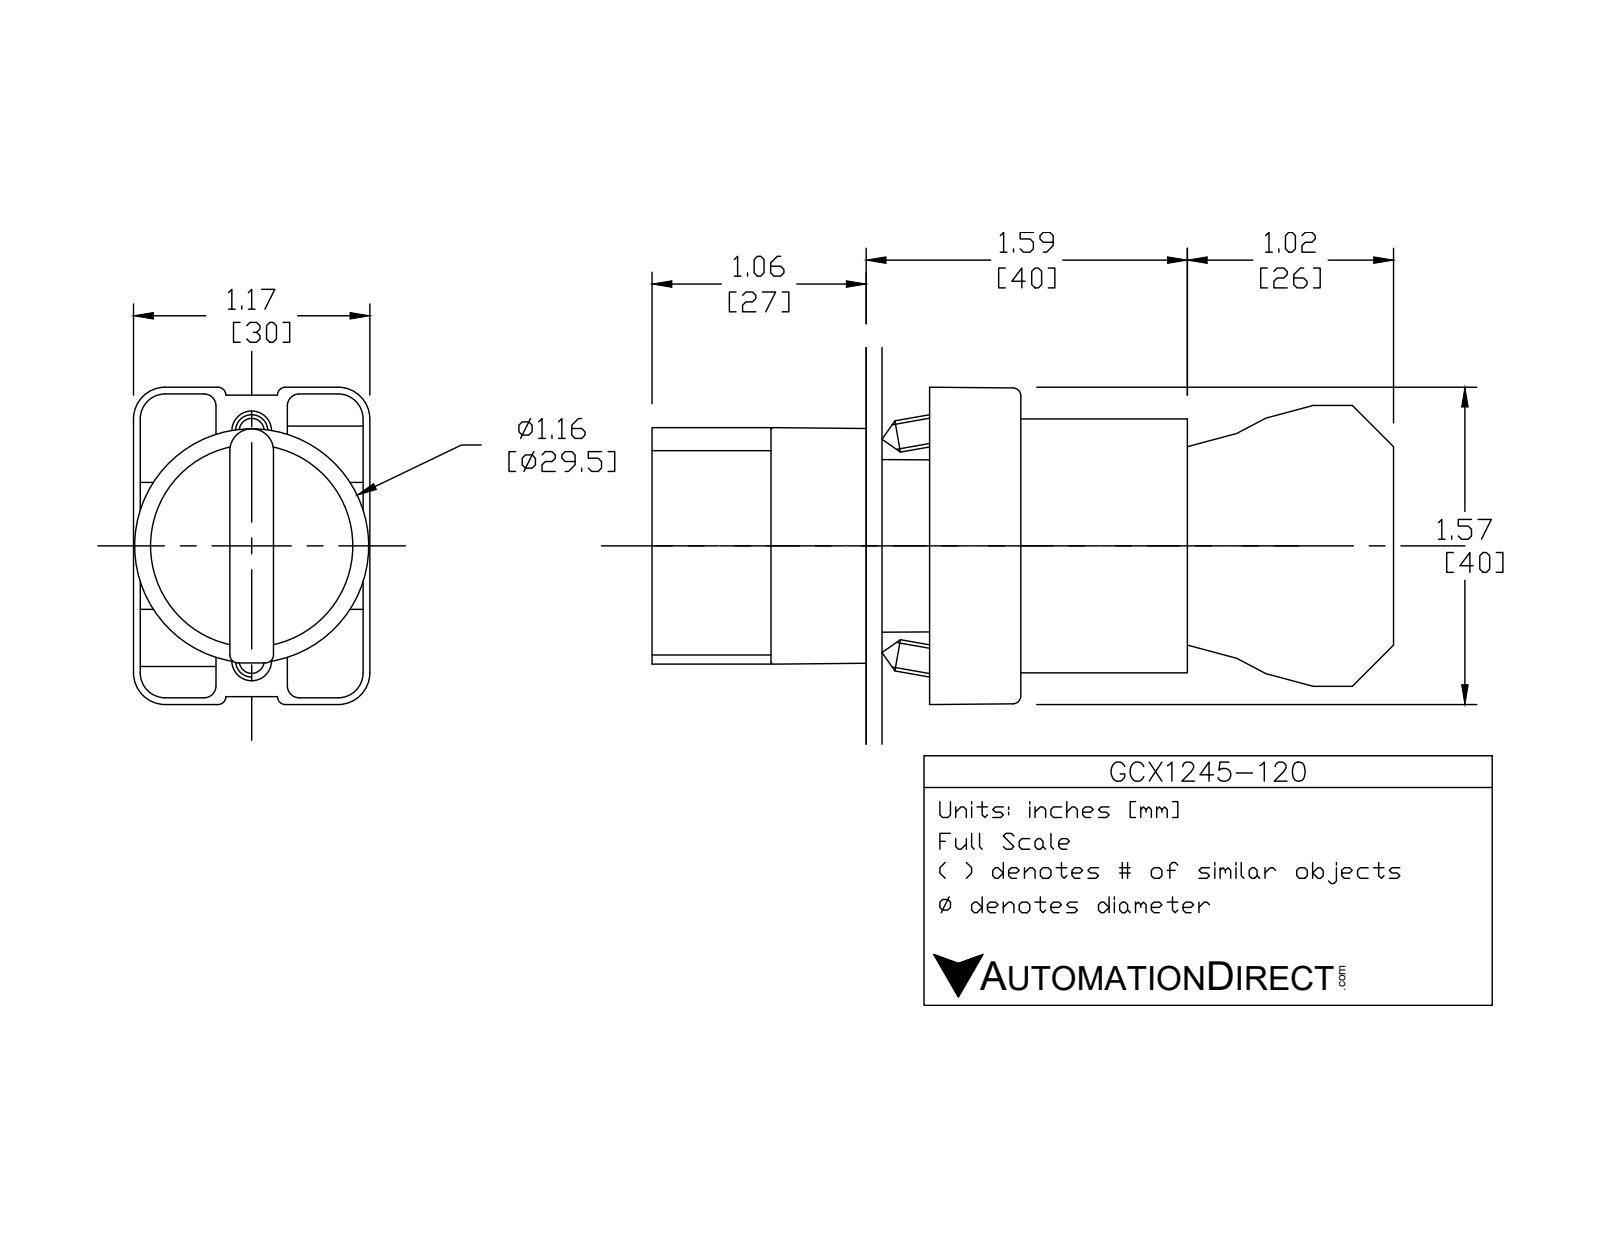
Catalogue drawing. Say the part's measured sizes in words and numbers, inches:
The part is named "ECX1050; ecx1040; GCX1245-120; ecx1029 (+1 more)". Its 3-D file was written by "SolidWorks 2016 (AUTOMOTIVE_DESIGN)". It is 8 solids with 445 faces: 263 planar, 151 cylindrical and 31 other. Overall it measures 3.653 by 1.581 by 1.177 inches. Its volume is 2.799 cubic inches and its surface area 39 square inches. Round holes: 2 of diameter 0.079, 2 of diameter 0.124, 2 of diameter 0.13, 1 of diameter 0.087, 1 of diameter 0.197, 1 of diameter 0.469, 1 of diameter 0.878, 1 of diameter 0.888, 1 of diameter 1.024. Round bosses or shafts: 4 of diameter 0.157, 1 of diameter 1.175, 1 of diameter 1.004, 1 of diameter 0.945, 1 of diameter 0.856, 1 of diameter 0.78, 1 of diameter 0.504. Partial cylindrical surfaces (rounded edges, fillets, slot ends): 24 of radius 0.059, 12 of radius 0.041, 12 of radius 0.124, 12 of radius 0.157, 9 of radius 0.039, 2 of radius 0.128, 1 of radius 0.02, 1 of radius 0.063. The main face-to-face distances are 0.827, 2.02, 1.193, 0.579, 1.244, 1.171, 0.472, 0.469, 0.031, 0.033. The hole center spacings are 0.236, 0.544, 0.472, 0.49.
